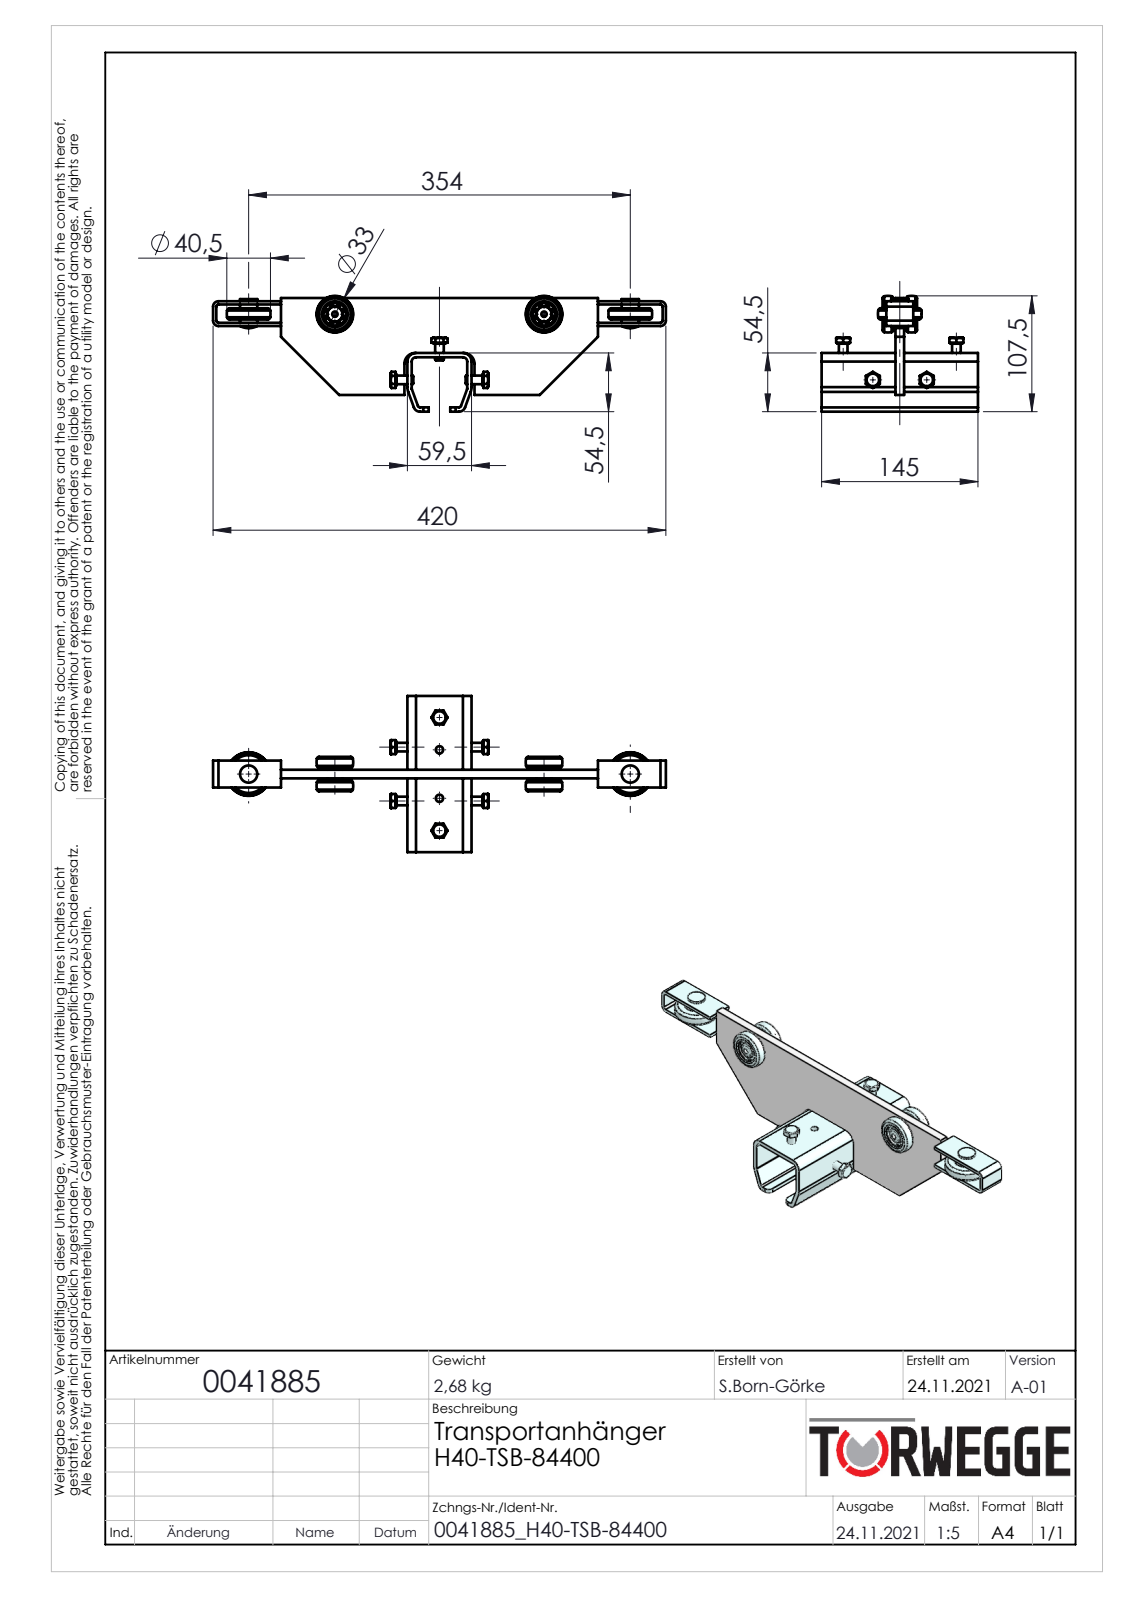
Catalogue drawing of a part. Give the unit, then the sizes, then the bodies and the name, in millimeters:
Units: millimetres
Overall size (bounding box): 420 × 145 × 107.5
Round holes (diameter × count): ⌀6.8 ×6, ⌀10 ×4, ⌀10.1 ×4, ⌀21.2 ×4, ⌀26 ×4, ⌀5 ×2, ⌀10.2 ×2, ⌀10.3 ×2, ⌀23 ×2, ⌀24 ×2
Round bosses / shafts (diameter × count): ⌀14.8 ×4, ⌀11.6 ×4, ⌀9.9 ×4, ⌀8 ×4, ⌀16 ×2, ⌀14 ×2
Partial cylindrical surfaces — rounded edges, fillets, slot ends (radius × count): R2 ×8, R5 ×8, R4 ×2, R6 ×2, R8 ×2, R10 ×2, R13 ×2
Main face-to-face distances: 8, 4, 3, 20, 55.5, 23, 50.5, 25, 17, 32
Hole centre spacings: 178.42, 184.62, 30, 75, 45, 50, 105, 194
Volume: 352 041 mm³ · Surface area: 167 253 mm²
Bodies: 88 solids, 688 faces (180 planar, 226 cylindrical, 282 other)
Part name (STEP PRODUCT): 0041885
STEP written by: SolidWorks 2020 (AUTOMOTIVE_DESIGN)
